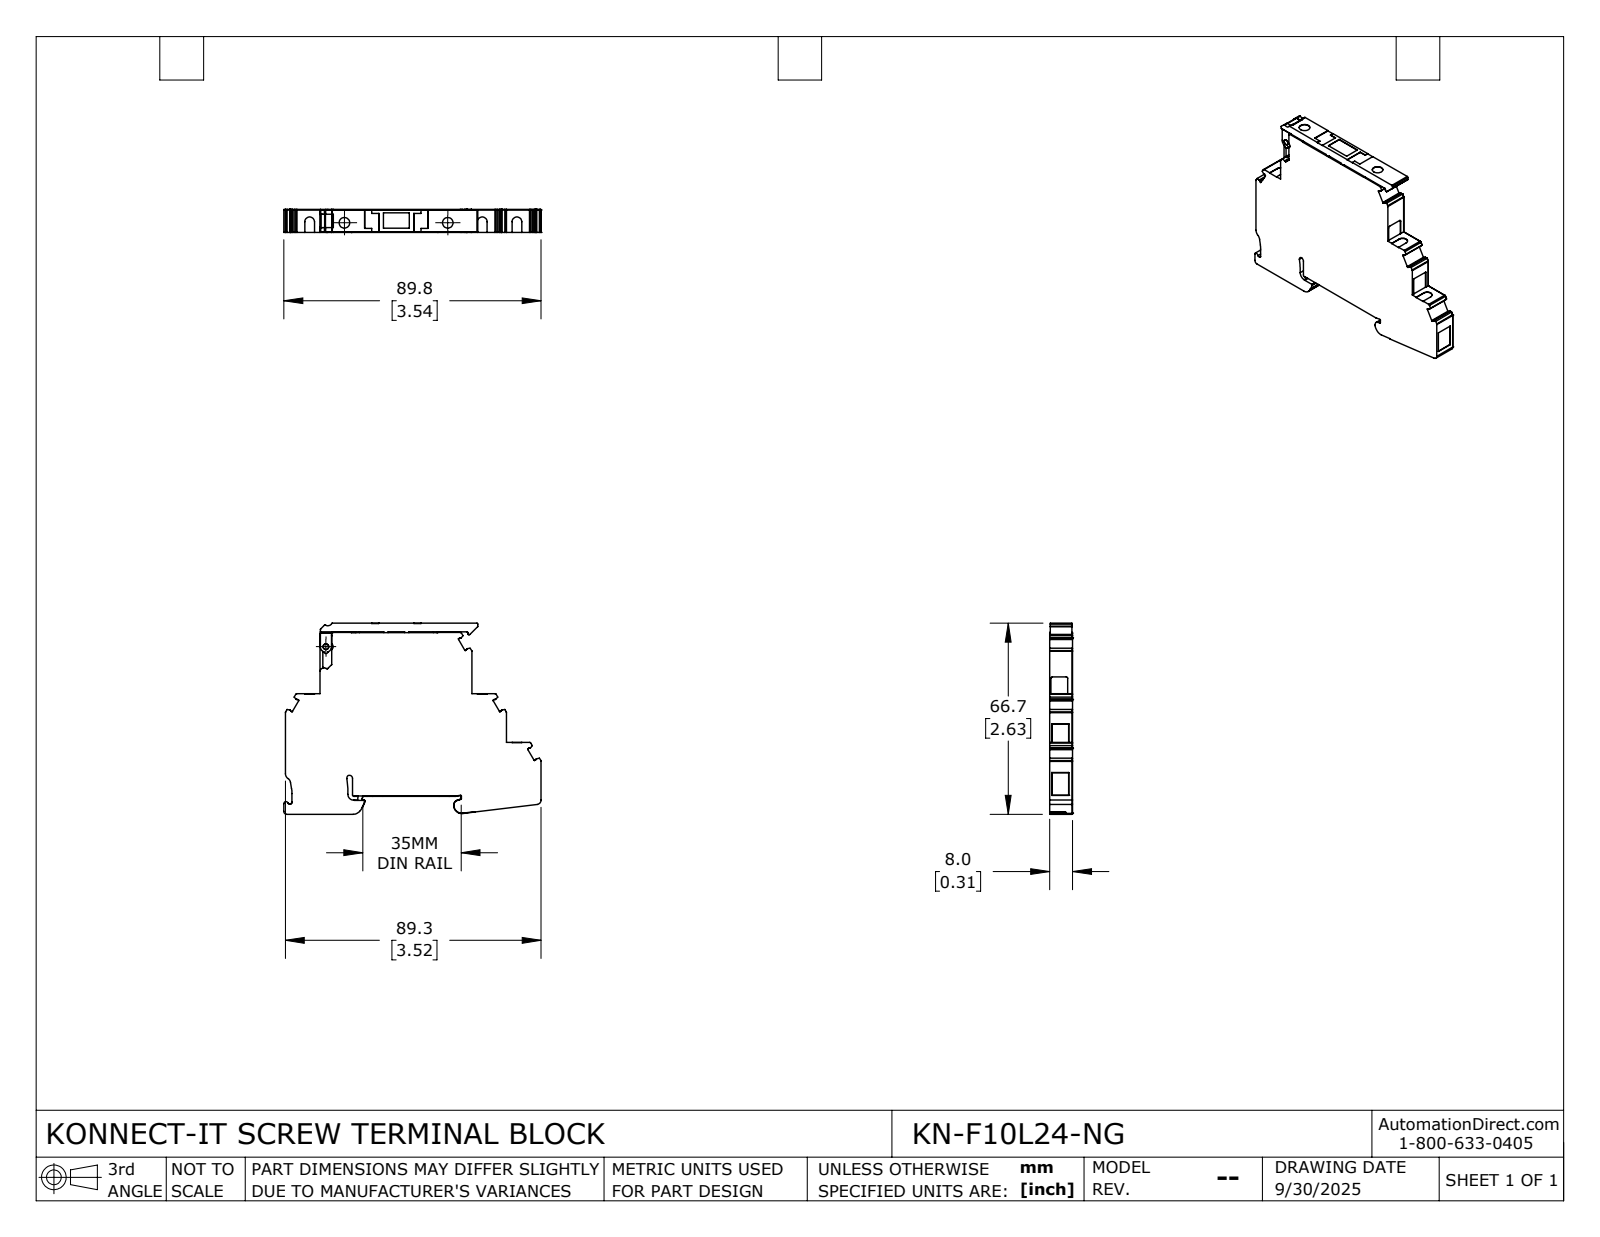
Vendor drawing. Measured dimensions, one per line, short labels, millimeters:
name: KN-F10L24-NG
written by: SolidWorks 2024 (CONFIG_CONTROL_DESIGN)
unit: mm
bodies: 1 solid, 530 faces (292 planar, 233 cylindrical, 5 other)
size: 89.85 × 66.7 × 8
volume: 35 374 mm³; area: 12 816 mm²
holes: 2× ⌀3.7, 2× ⌀4.3, 1× ⌀2
bosses: 1× ⌀1.9
rounds: 31× R0.5, 29× R0.3, 17× R0.4, 9× R0.1, 8× R0.26, 6× R0.2, 6× R1, 3× R0.9
face distances: 8, 7.8, 12.1, 57.14, 3.3, 3.2, 3, 60.34, 57.44, 2.9
hole spacings: 36.1, 36.05, 36.15
